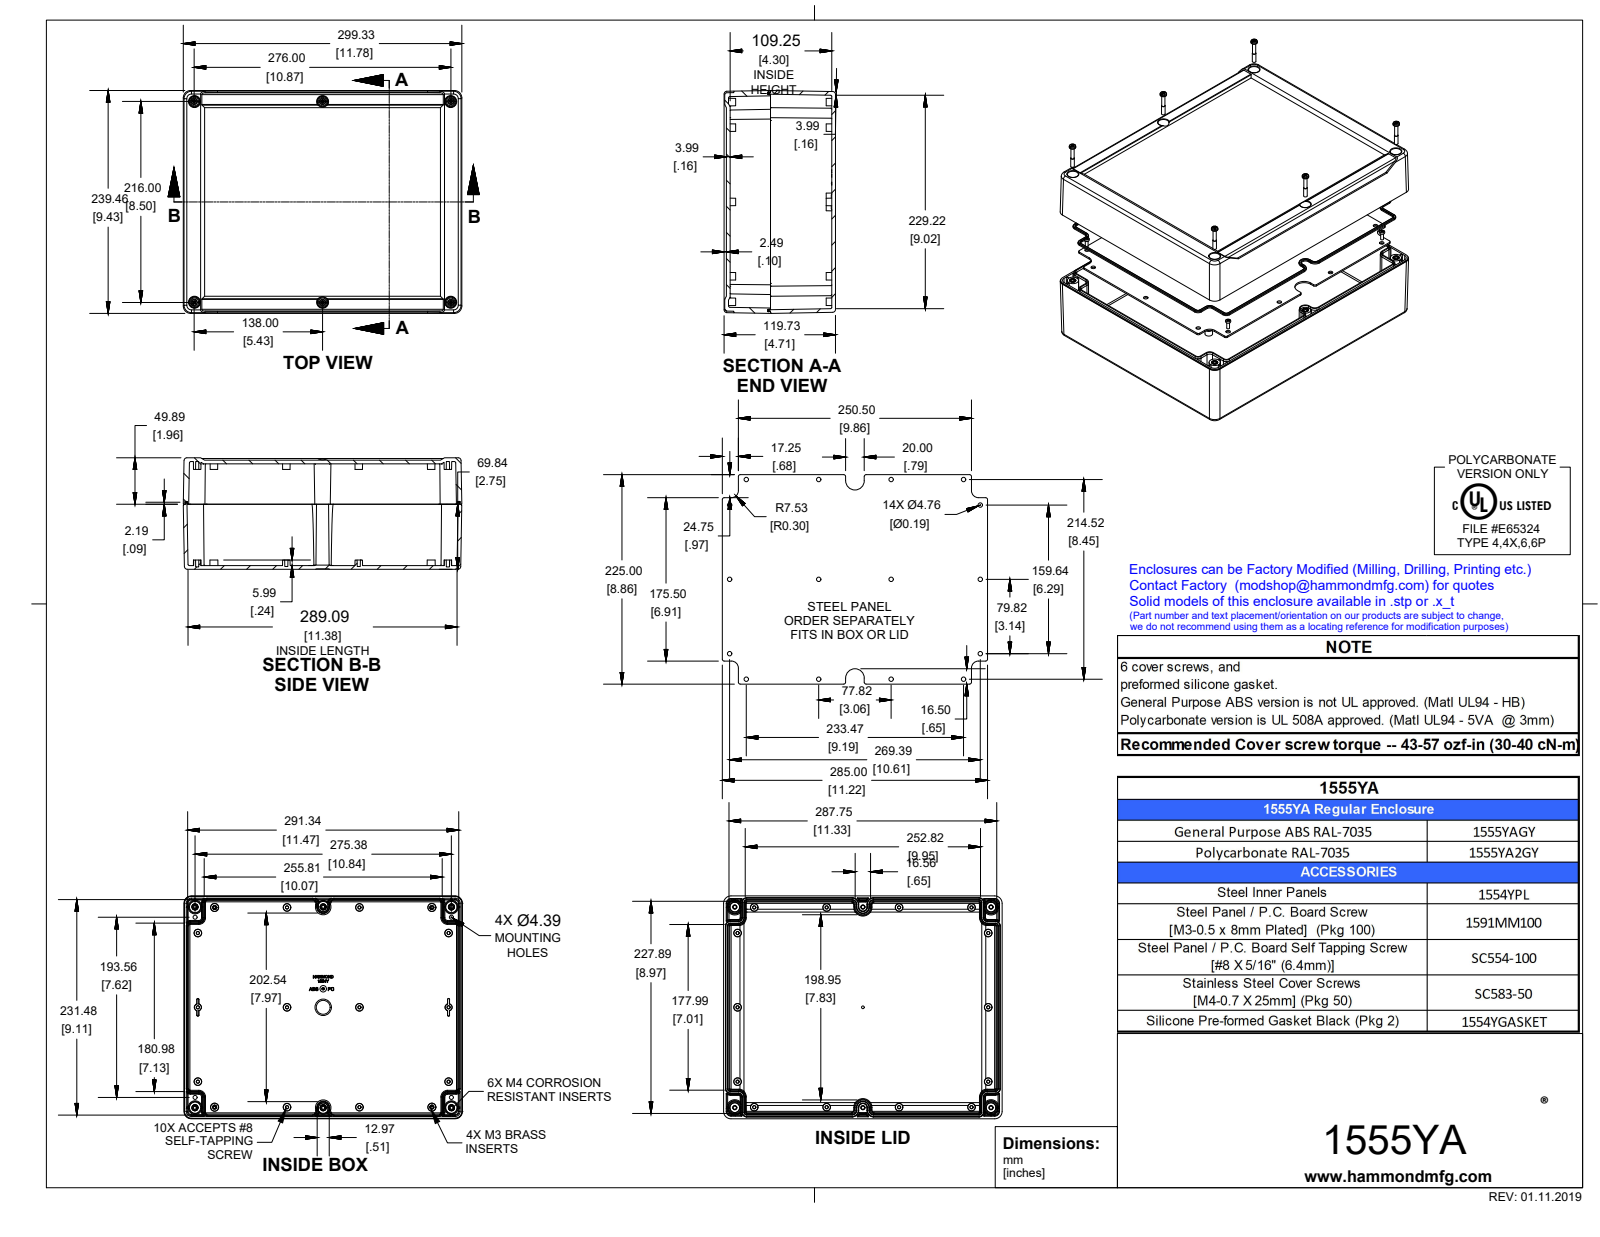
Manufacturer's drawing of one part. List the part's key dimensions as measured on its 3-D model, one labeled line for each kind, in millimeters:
Part name (STEP PRODUCT): 1555YA2GY
STEP written by: SolidWorks 2019 (AUTOMOTIVE_DESIGN)
Units: millimetres
Bodies: 24 solids, 3317 faces (956 planar, 722 cylindrical, 1639 other)
Overall size (bounding box): 300 × 240 × 120
Volume: 1 288 000 mm³ · Surface area: 760 600 mm²
Round holes (diameter × count): ⌀4.7 ×16, ⌀3.3 ×6, ⌀3.6 ×6, ⌀2.5 ×4, ⌀7 ×1
Round bosses / shafts (diameter × count): ⌀6.9 ×6, ⌀6.4 ×6, ⌀5.4 ×6, ⌀5.3 ×6, ⌀3.9 ×6, ⌀3.5 ×6, ⌀3 ×5, ⌀4.8 ×4
Partial cylindrical surfaces — rounded edges, fillets, slot ends (radius × count): R0.5 ×30, R0.3 ×20, R0.8 ×14, R2 ×14, R0.7 ×12, R3 ×12, R1.2 ×8, R8 ×8
Main face-to-face distances: 4, 113.5, 6, 10, 1.6, 11.6, 7.6, 109.5, 103.5, 101.9
Hole centre spacings: 132.8, 78, 228.7, 21, 28.2, 32.9, 39, 80
